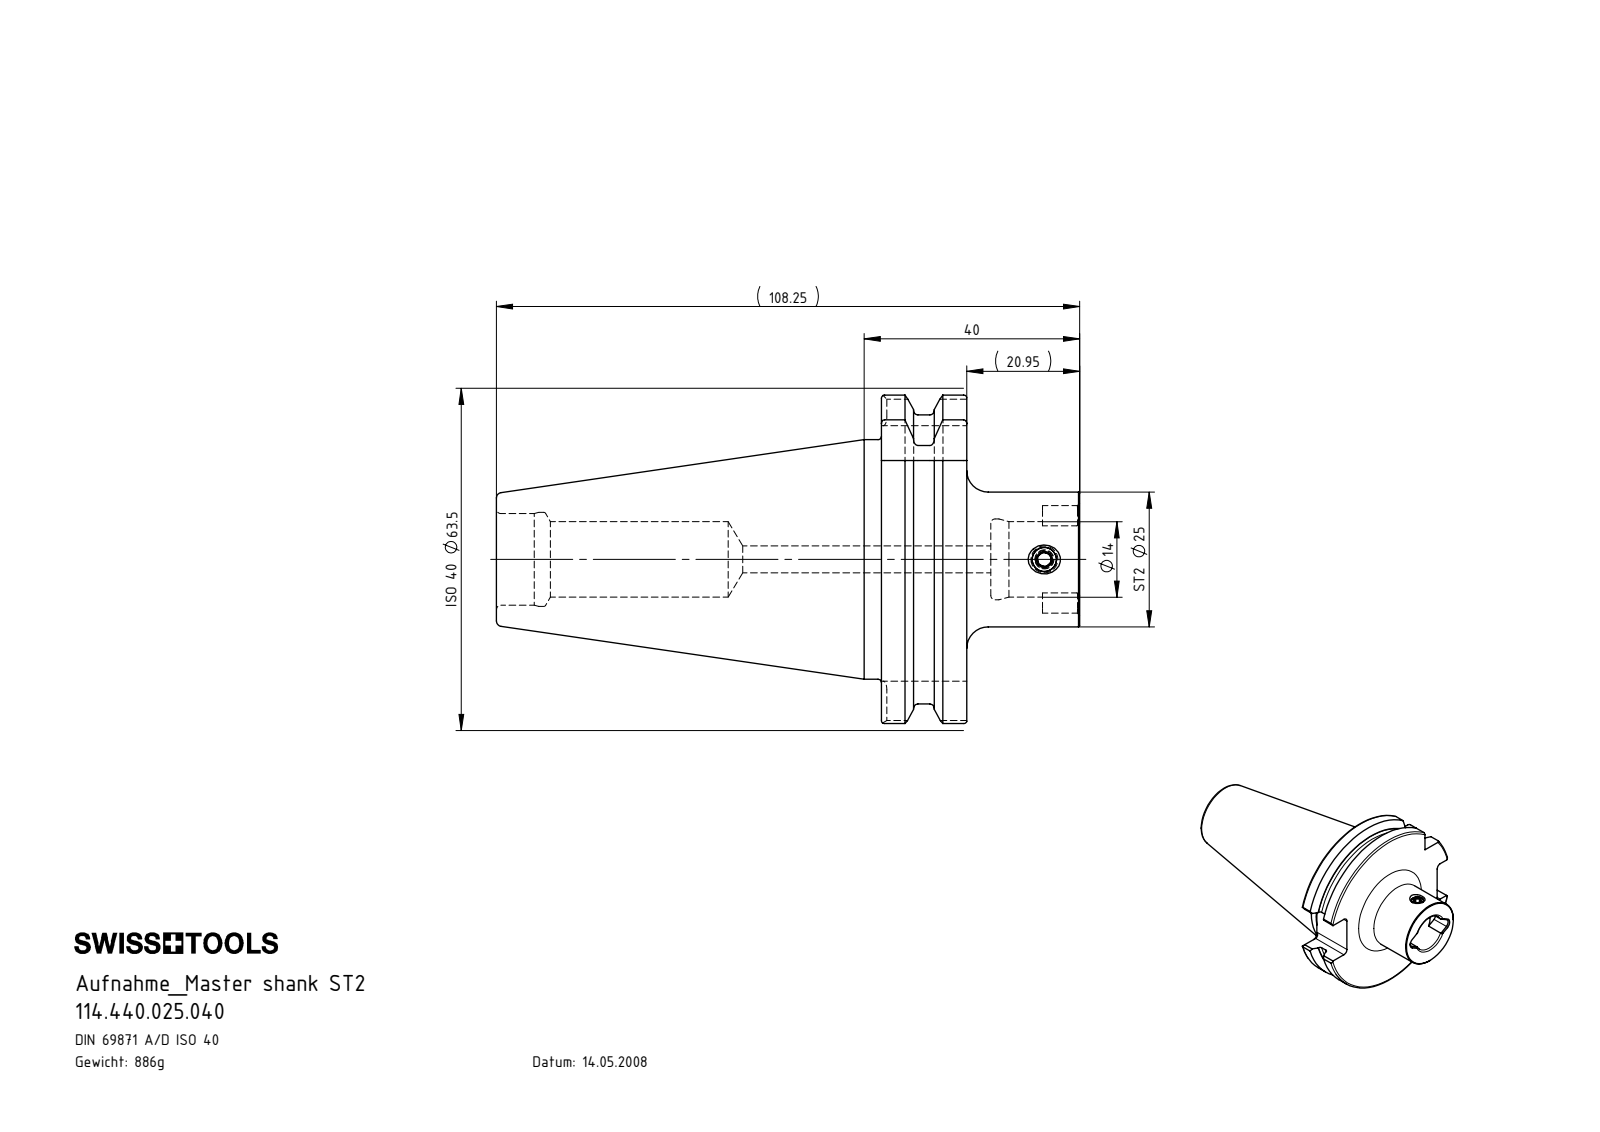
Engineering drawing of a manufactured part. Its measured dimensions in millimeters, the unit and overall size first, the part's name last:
Units: millimetres
Overall size (bounding box): 108.25 × 63.5 × 60.94
Round holes (diameter × count): ⌀2.5 ×1, ⌀4.5 ×1, ⌀5 ×1, ⌀14 ×1, ⌀15 ×1, ⌀17 ×1, ⌀17.45 ×1
Round bosses / shafts (diameter × count): ⌀44.45 ×1, ⌀25 ×1, ⌀5 ×1
Partial cylindrical surfaces — rounded edges, fillets, slot ends (radius × count): R1.6 ×8, R1.8 ×2, R28 ×1, R31.75 ×1
Main face-to-face distances: 15.85, 36.8, 20.95, 47.4, 71.45, 87.3, 108.25, 91.75, 20.3, 4.45
Volume: 112 862 mm³ · Surface area: 21 650 mm²
Bodies: 2 solids, 126 faces (54 planar, 30 cylindrical, 42 other)
Part name (STEP PRODUCT): SK4-ST2.K01.040_A; SK4.ST2.K01.040; ST2-ER1.001.006_A
STEP written by: SolidWorks 2017 (AUTOMOTIVE_DESIGN)
